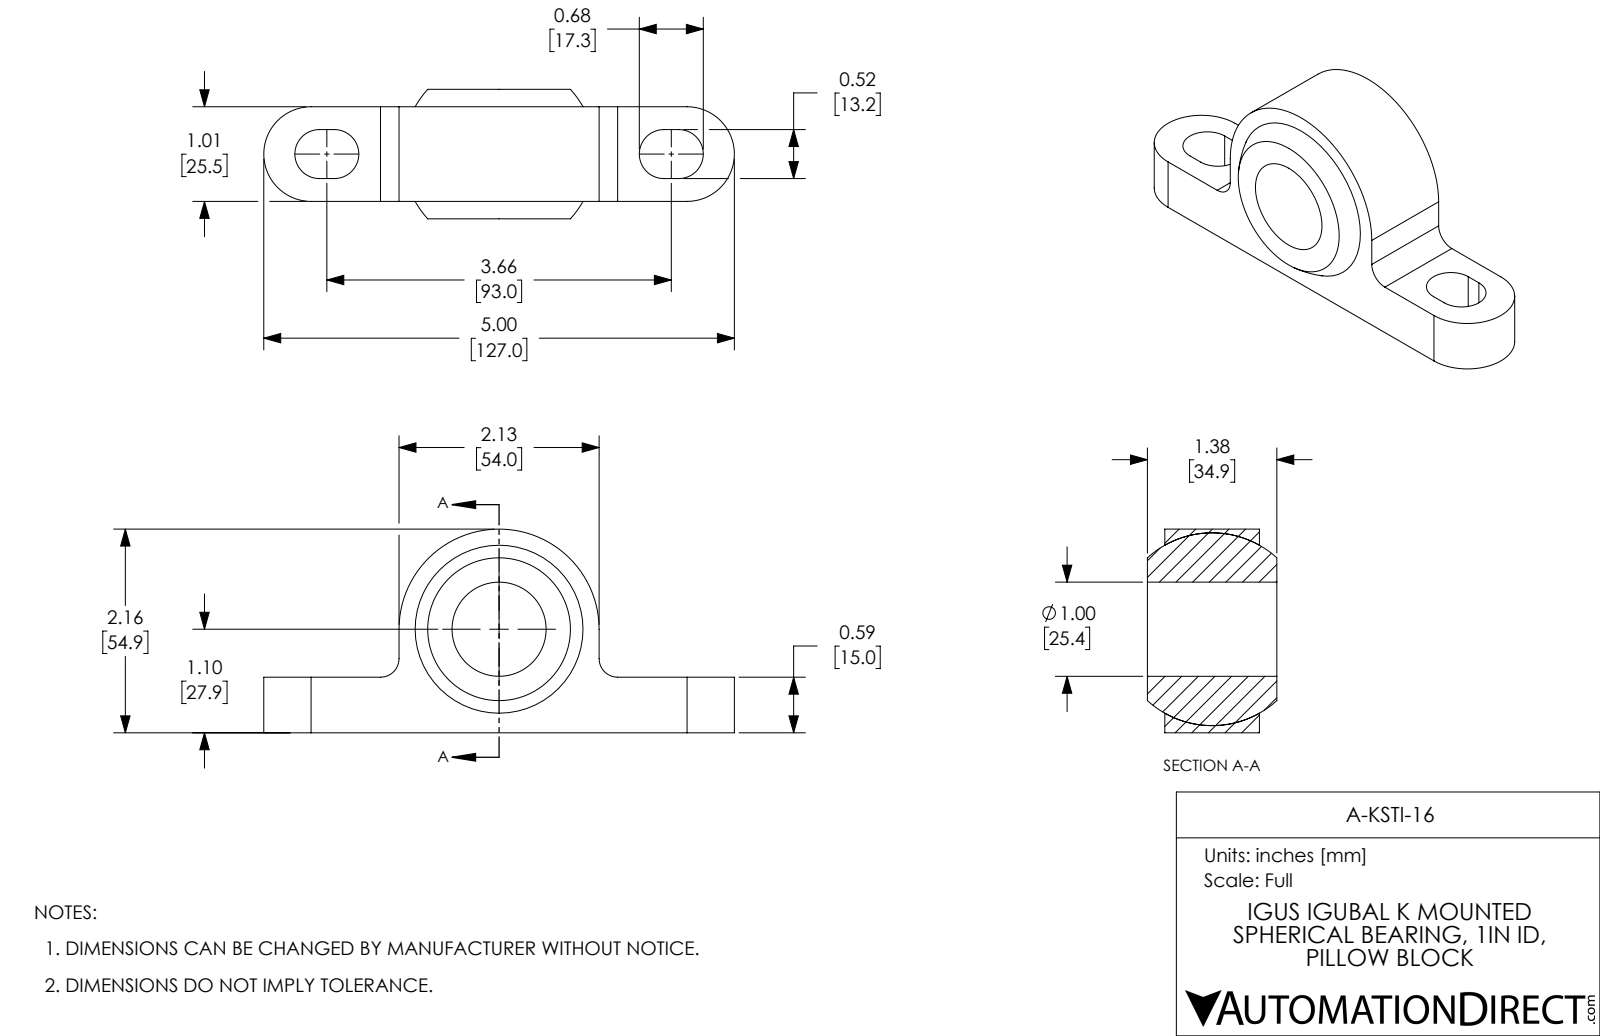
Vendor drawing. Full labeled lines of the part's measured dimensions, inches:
Part name (STEP PRODUCT): A-KSTI-16
STEP written by: SolidWorks 2017 (AUTOMOTIVE_DESIGN)
Units: inches
Bodies: 2 solids, 31 faces (13 planar, 14 cylindrical, 4 other)
Overall size (bounding box): 5 × 2.163 × 1.375
Volume: 5.103 in³ · Surface area: 41.82 in²
Round holes (diameter × count): ⌀1 ×1
Partial cylindrical surfaces — rounded edges, fillets, slot ends (radius × count): R0.26 ×4, R0.197 ×2, R0.503 ×2, R1.063 ×1
Main face-to-face distances: 1.006, 0.185, 1.19, 0.591, 1.375, 0.427, 0.948, 0.243, 0.763, 2.126
